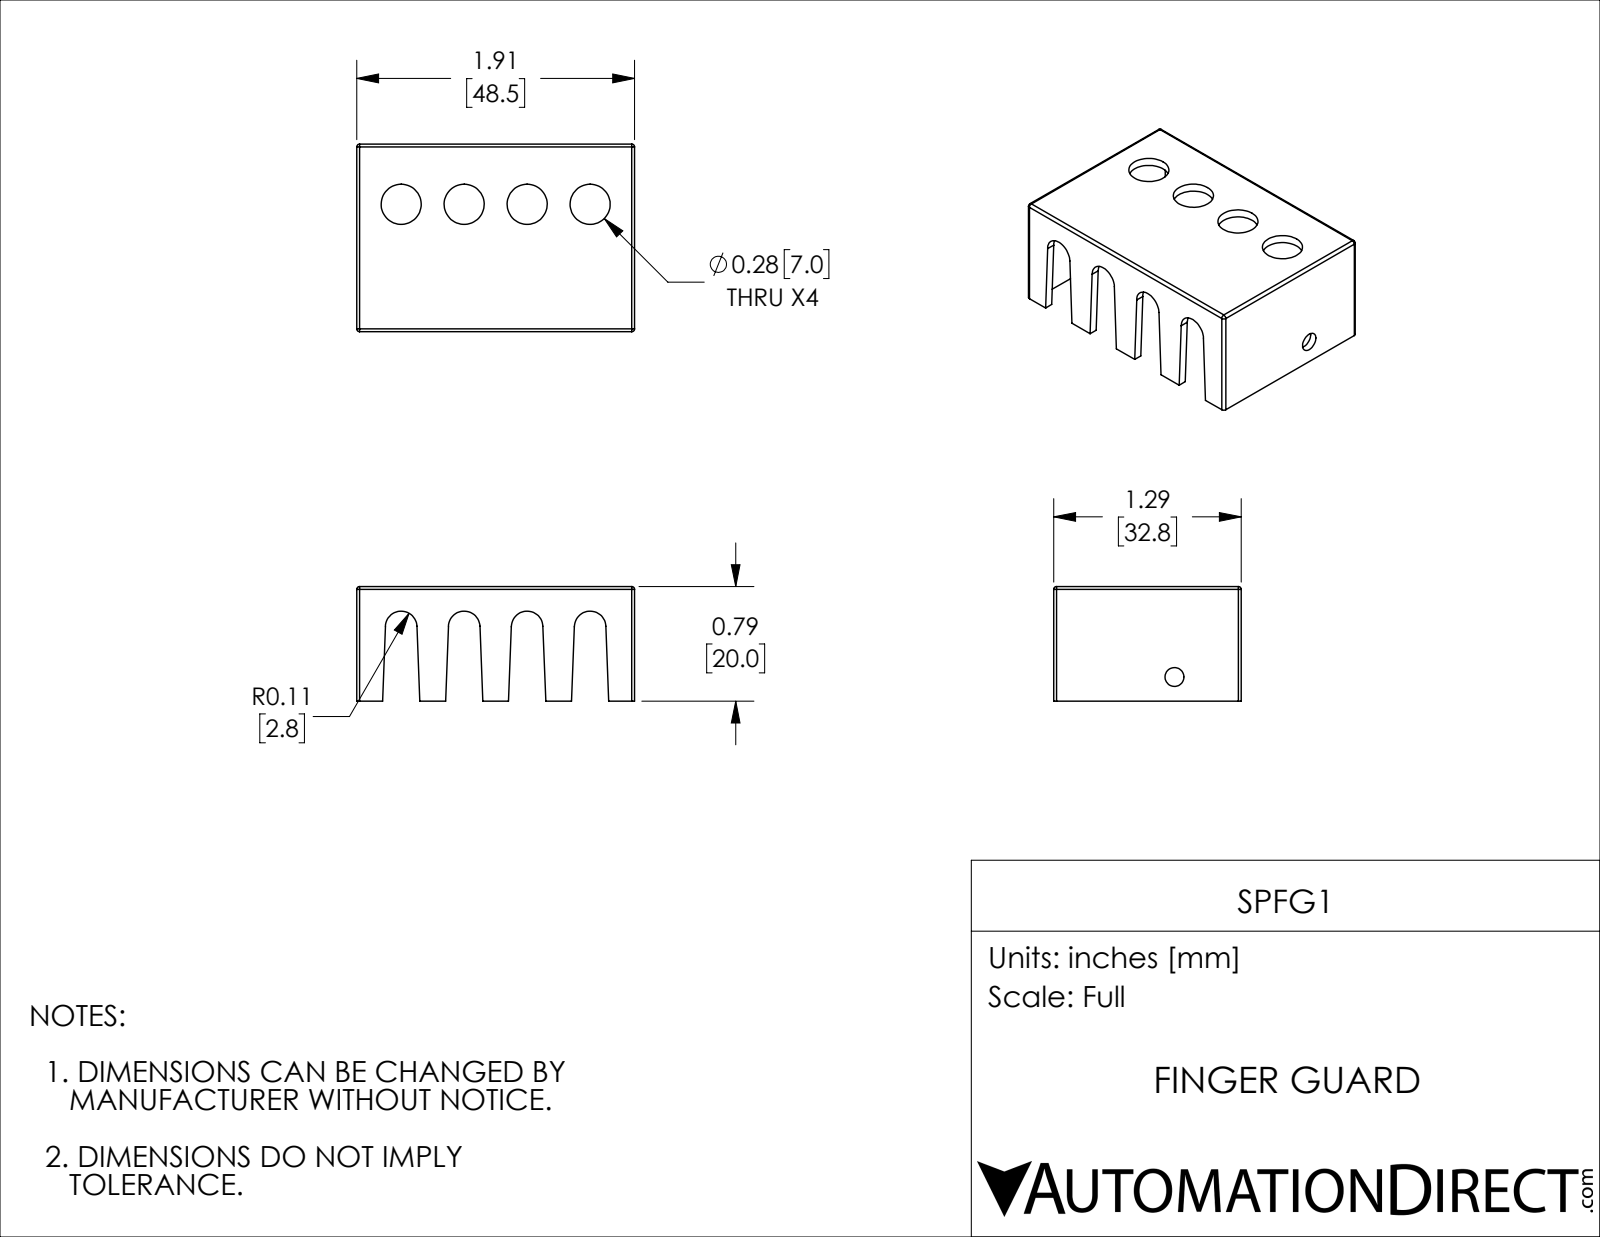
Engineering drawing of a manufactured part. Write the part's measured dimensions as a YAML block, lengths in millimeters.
part_name: "SPFG1"
step_written_by: "SolidWorks 2018 (AUTOMOTIVE_DESIGN)"
units: millimeters
bodies: {solids: 1, faces: 52, planar: 24, cylindrical: 24, other: 4}
overall_size: [48.5, 32.75, 20]
volume: 4553
surface_area: 6986
round_holes:
  - {diameter: 7, count: 4}
  - {diameter: 3.3, count: 1}
partial_cylinders:
  - {radius: 0.5, count: 8}
  - {radius: 2.75, count: 4}
face_to_face_distances: [1.5, 1.3, 47.2, 48.5, 45.9, 32.75, 31.25, 18.5, 20, 10.99]
hole_center_spacings: [11, 22, 33]
